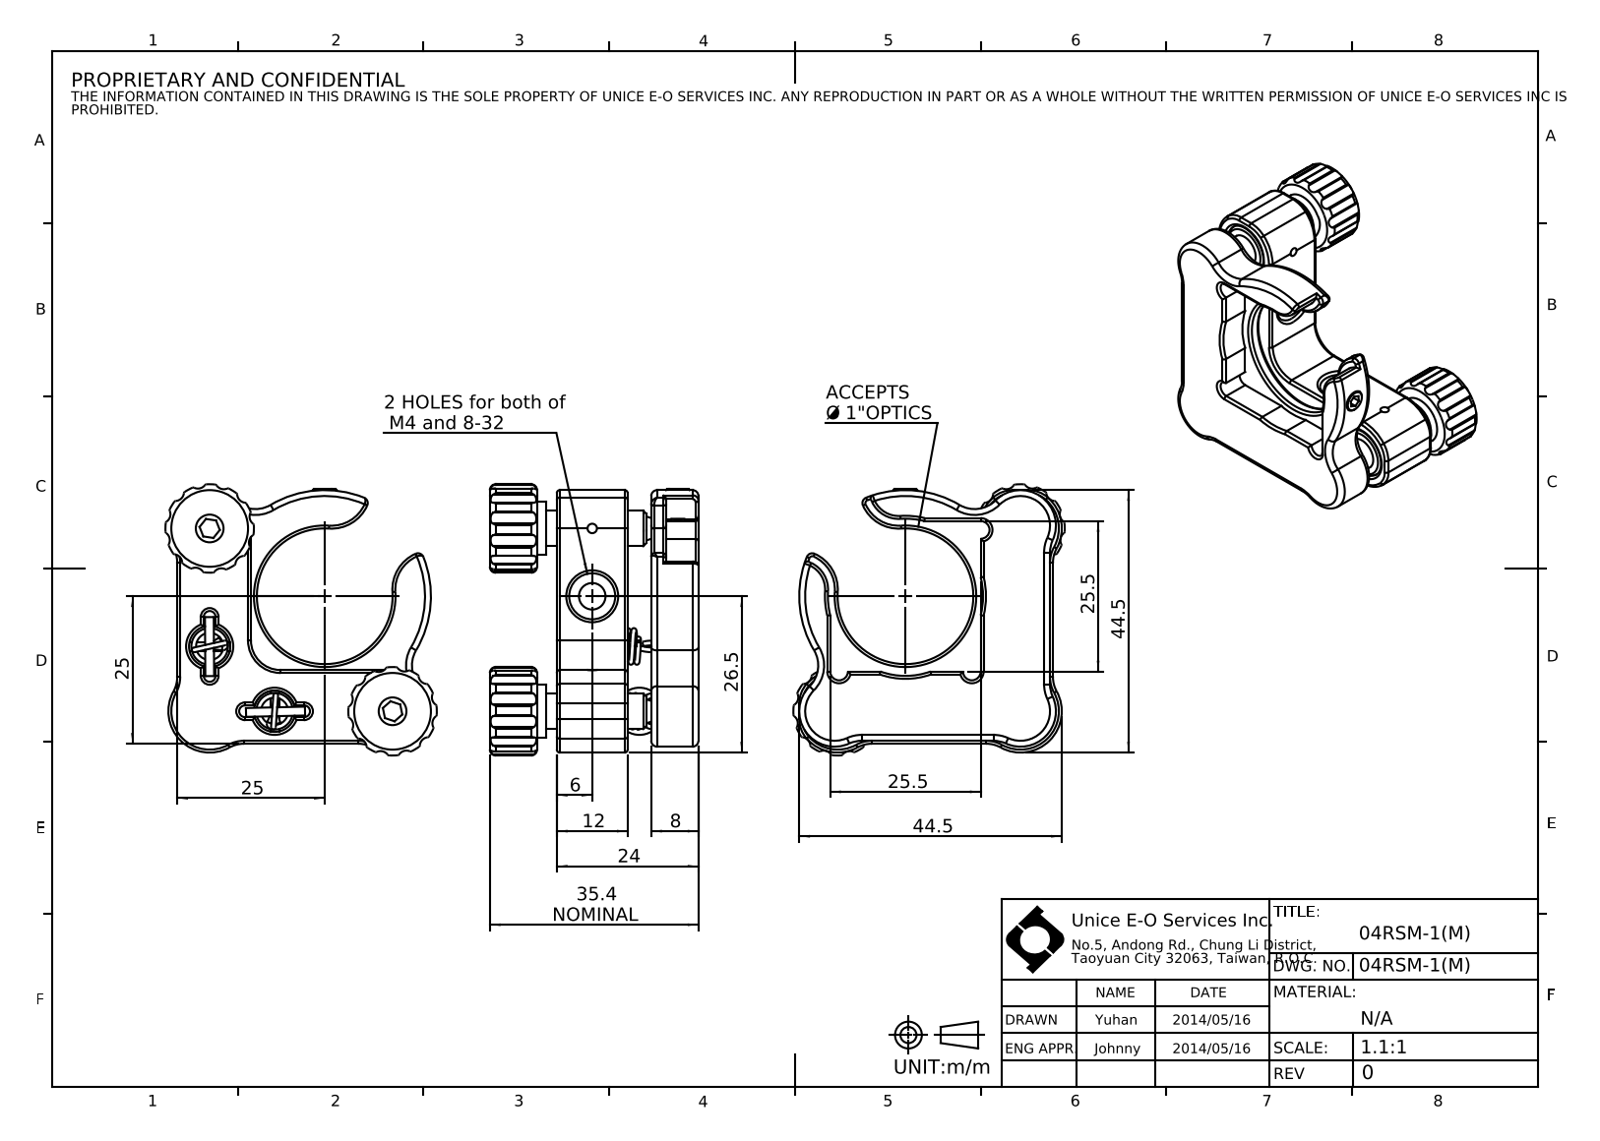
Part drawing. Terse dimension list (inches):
name: 04RSM-1(M)
written by: SolidWorks 2016 (CONFIG_CONTROL_DESIGN)
unit: in
bodies: 22 solids, 618 faces (114 planar, 300 cylindrical, 204 other)
size: 1.811 × 1.811 × 1.392
volume: 1.256 in³; area: 24.07 in²
holes: 4× ⌀0.043, 2× ⌀0.063, 2× ⌀0.067, 2× ⌀0.157, 2× ⌀0.177, 2× ⌀0.185, 2× ⌀0.232, 2× ⌀0.236, 2× ⌀0.276, 2× ⌀0.307, 2× ⌀0.374, 1× ⌀0.059
bosses: 6× ⌀0.059, 2× ⌀0.354, 2× ⌀0.031, 1× ⌀0.157, 1× ⌀0.063
rounds: 48× R0.012, 28× R0.059, 22× R0.02, 17× R0.197, 10× R0.039, 4× R0.03, 3× R0.236, 3× R0.276
face distances: 0.472, 0.315, 0.157, 0.63, 0.945, 1.077, 0.217, 0.098, 0.492, 0.919
hole spacings: 0.453, 0.679, 0.787, 0.984, 1.295, 0.335, 0.571, 0.613
